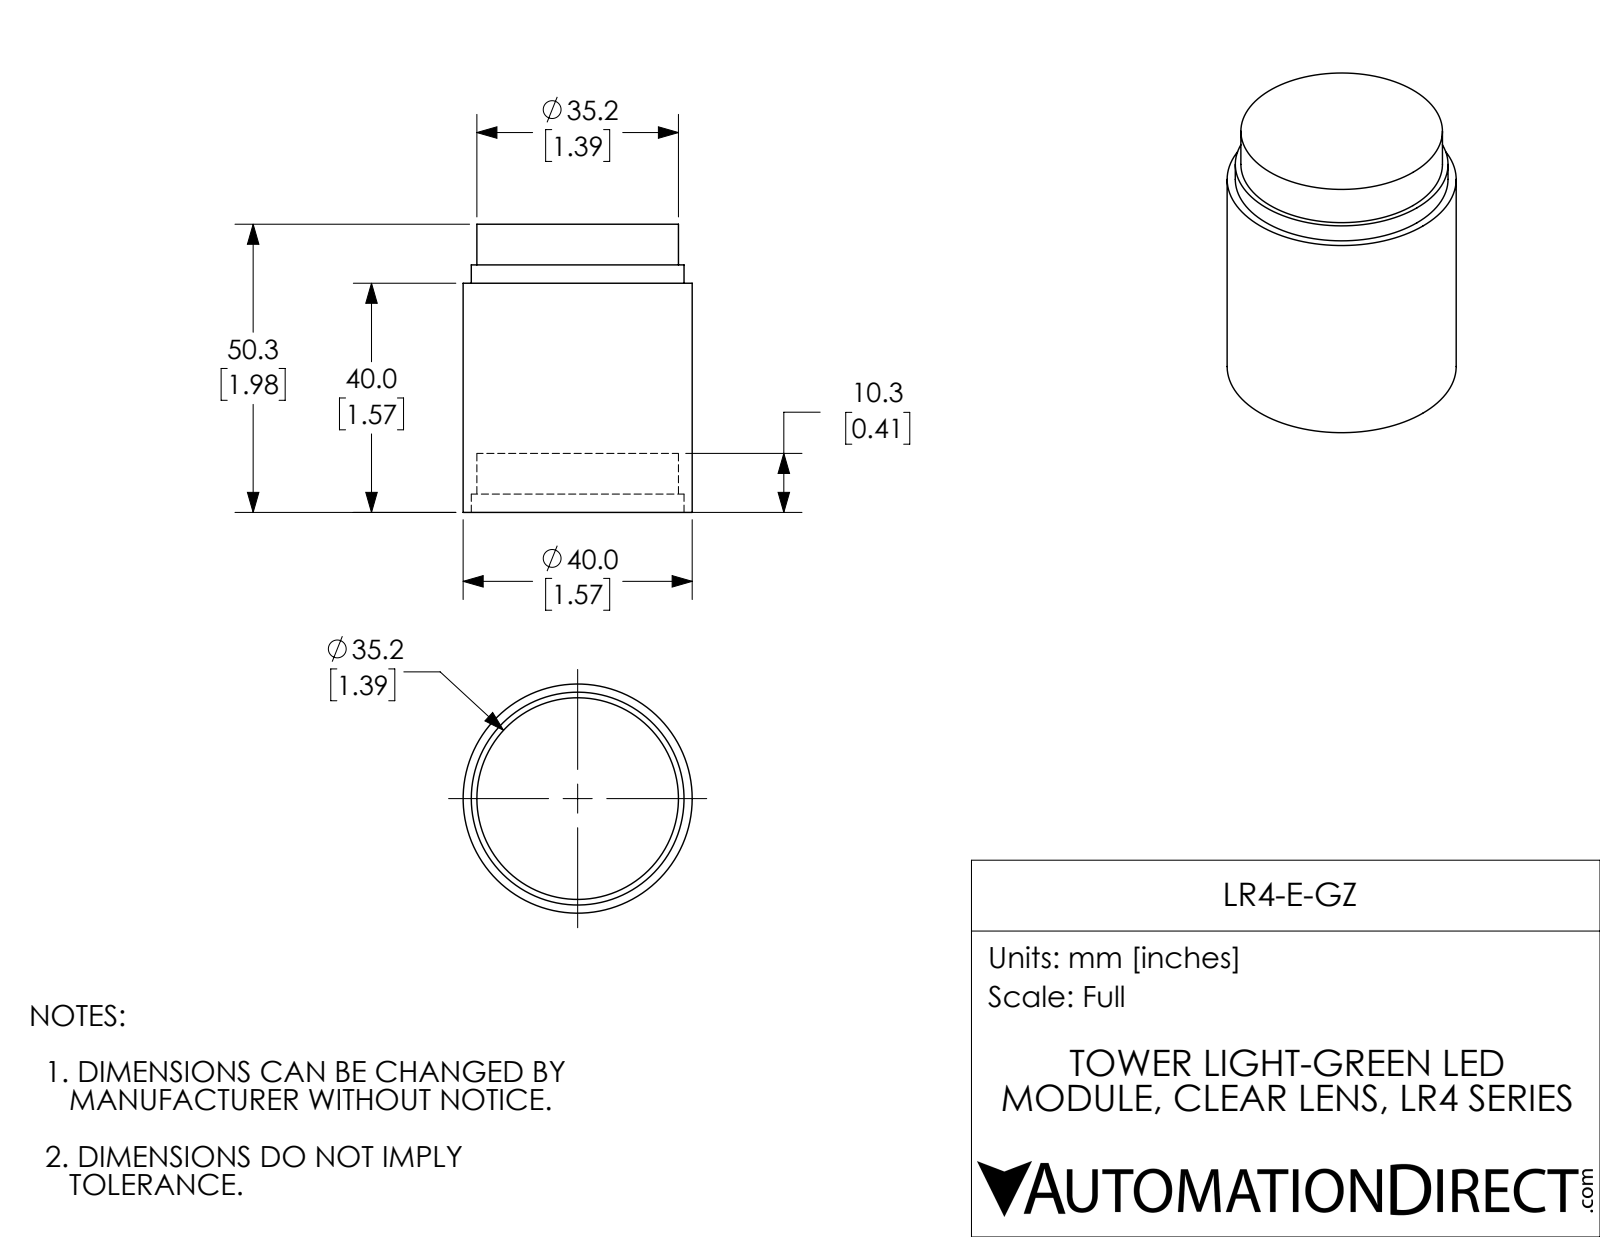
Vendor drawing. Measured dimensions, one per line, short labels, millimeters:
name: LR4-E-GZ
written by: SolidWorks 2017 (AUTOMOTIVE_DESIGN)
unit: mm
bodies: 1 solid, 16 faces (6 planar, 10 cylindrical, 0 other)
size: 50.3 × 40 × 40
volume: 50 260 mm³; area: 9 858 mm²
holes: 1× ⌀35.2, 1× ⌀37.2
bosses: 1× ⌀40
face distances: 40, 10.3, 3.2, 7.1, 50.3, 29.7, 43.2, 32.9, 36.8, 47.1
